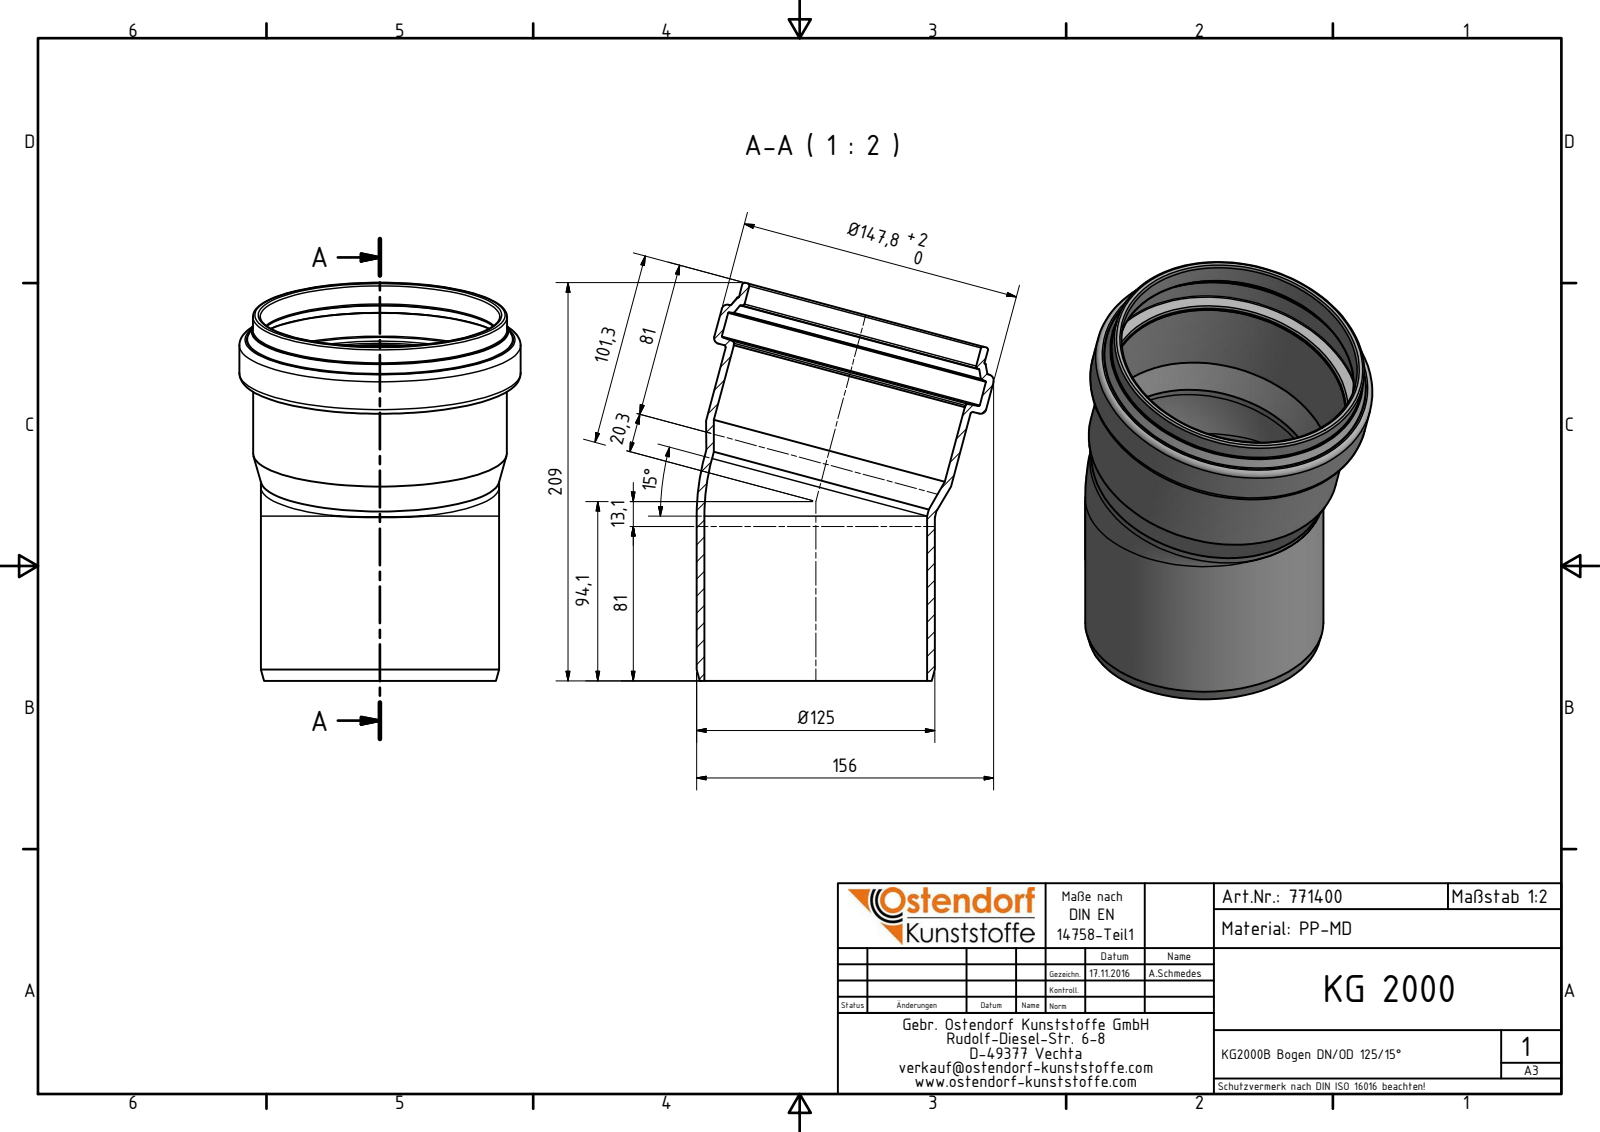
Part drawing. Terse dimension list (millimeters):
name: 771400 KG2000B Bogen DN_OD 125_15°
written by: Autodesk Inventor 2016 (AUTOMOTIVE_DESIGN)
unit: mm
bodies: 1 solid, 42 faces (5 planar, 11 cylindrical, 26 other)
size: 209 × 156 × 147.8
volume: 321 058 mm³; area: 165 743 mm²
holes: 2× ⌀116.9, 2× ⌀125.9, 1× ⌀125.6, 1× ⌀140.2
bosses: 2× ⌀125.1, 1× ⌀147.8, 1× ⌀133.5, 1× ⌀133.2
face distances: 34.5, 21.1, 13.4, 1.28, 19.82, 33.22
